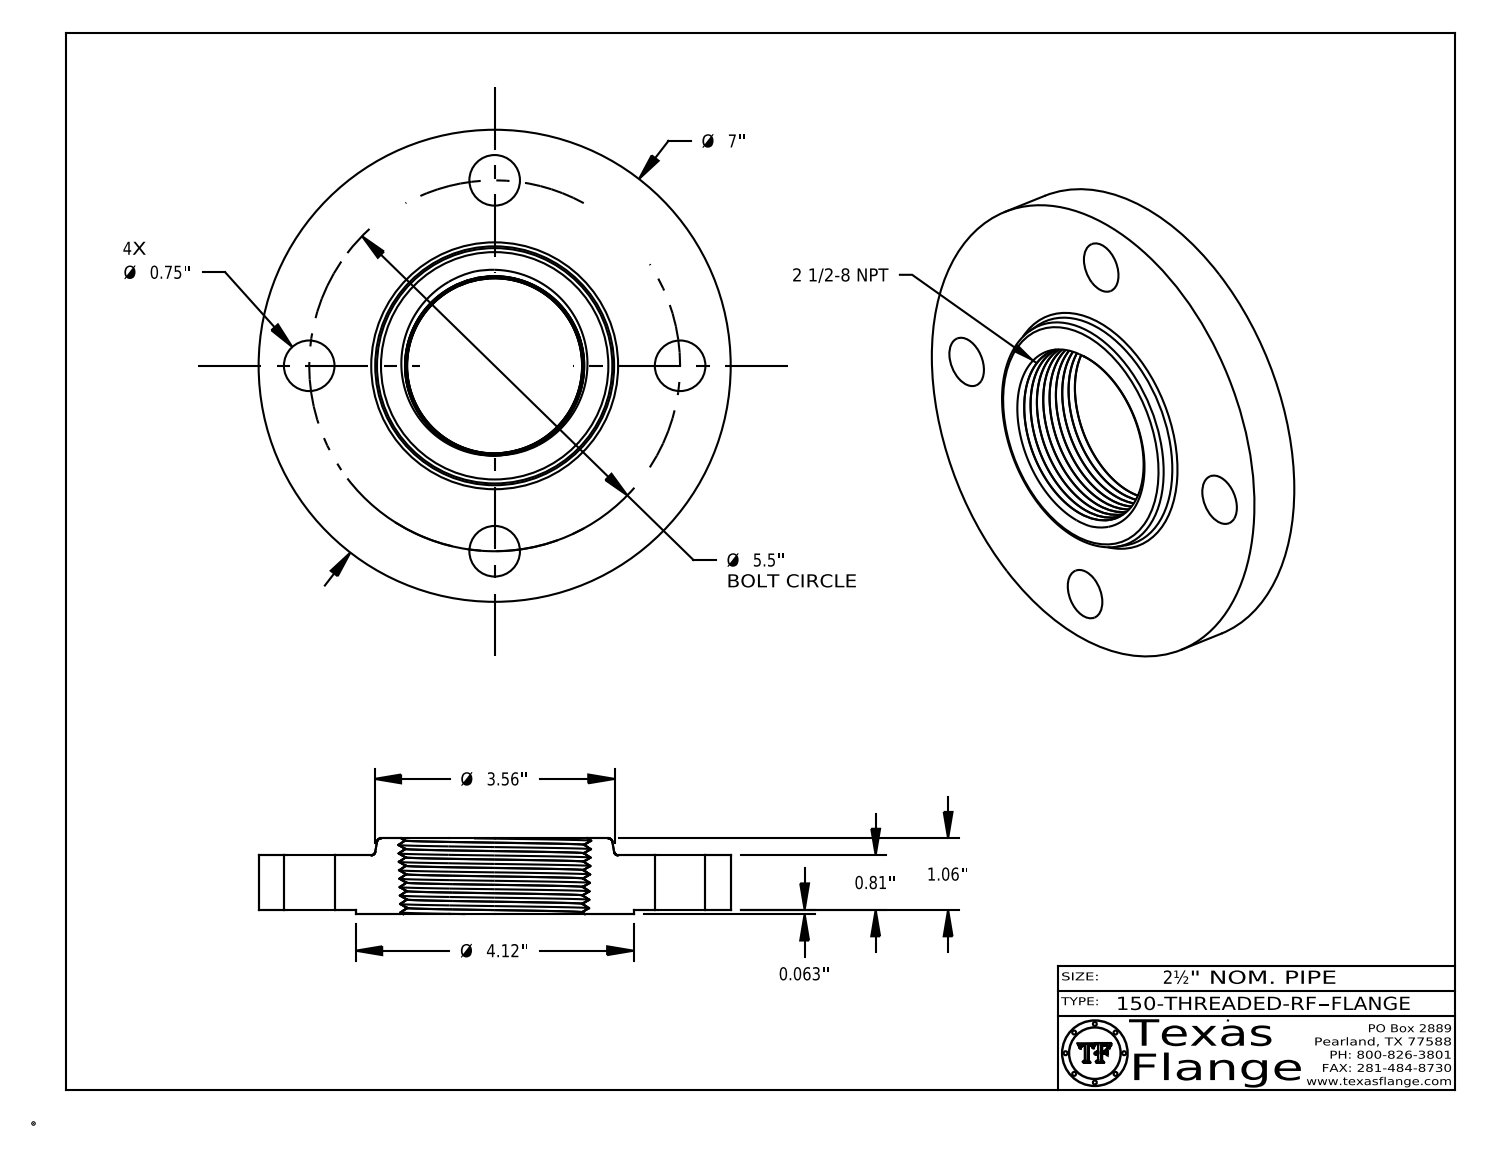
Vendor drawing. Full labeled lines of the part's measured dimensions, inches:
Part name (STEP PRODUCT): 150-THREADED-RF
STEP written by: CATIA V5 STEP AP214 (AUTOMOTIVE_DESIGN)
Units: inches
Bodies: 1 solid, 504 faces (369 planar, 32 cylindrical, 103 other)
Overall size (bounding box): 7 × 7 × 1.123
Volume: 26.46 in³ · Surface area: 108.1 in²
Round holes (diameter × count): ⌀0.75 ×4, ⌀0.495 ×1
Round bosses / shafts (diameter × count): ⌀0.03 ×8, ⌀7 ×1, ⌀4.12 ×1, ⌀0.39 ×1
Main face-to-face distances: 0.81, 0.063, 0.872, 1.122, 1.06, 0.25, 0.857, 0.795, 0.015, 0.265
Hole centre spacings: 3.889, 2.105, 5.081, 5.5
